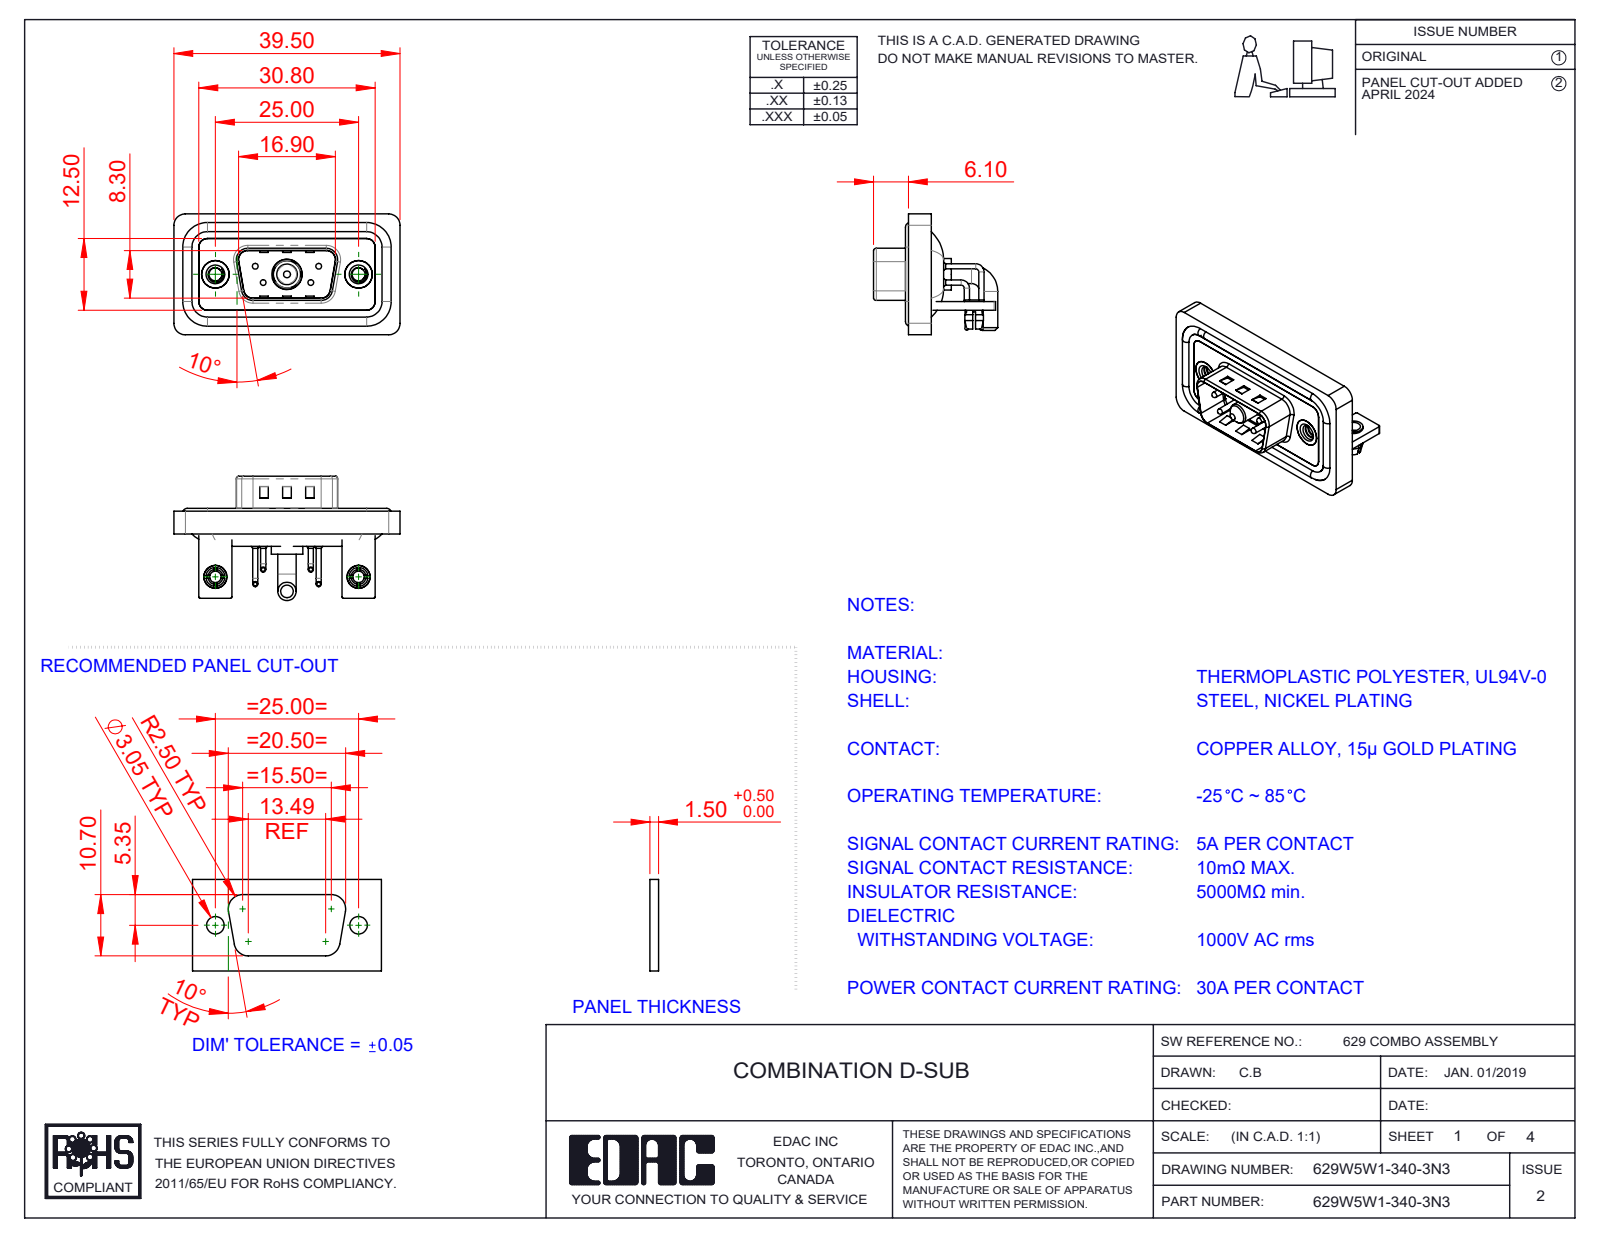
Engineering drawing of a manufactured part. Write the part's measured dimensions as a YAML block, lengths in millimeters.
part_name: "629Combo Waterproof Housing_09 Contacts; Power Pin_30A RA; 629Combo Housing_5W1; 629Combo Stabilizer Bracket (+7 more)"
step_written_by: "SolidWorks 2023 (CONFIG_CONTROL_DESIGN)"
units: millimeters
bodies: {solids: 17, faces: 1026, planar: 479, cylindrical: 395, other: 152}
overall_size: [39.5, 21.7, 21.1]
volume: 4818
surface_area: 7979
round_holes:
  - {diameter: 2, count: 6}
  - {diameter: 0.75, count: 4}
  - {diameter: 1.6, count: 4}
  - {diameter: 2.26, count: 2}
  - {diameter: 2.5, count: 2}
  - {diameter: 3.2, count: 2}
  - {diameter: 4, count: 2}
  - {diameter: 4.8, count: 2}
  - {diameter: 5, count: 2}
  - {diameter: 4.85, count: 1}
  - {diameter: 5.3, count: 1}
round_bosses_or_shafts:
  - {diameter: 0.9, count: 8}
  - {diameter: 1.6, count: 4}
  - {diameter: 1.5, count: 4}
  - {diameter: 1, count: 4}
  - {diameter: 0.65, count: 4}
  - {diameter: 4.9, count: 2}
  - {diameter: 4, count: 2}
  - {diameter: 3.4, count: 2}
partial_cylinders:
  - {radius: 2, count: 19}
  - {radius: 1.5, count: 18}
  - {radius: 0.25, count: 16}
  - {radius: 0.5, count: 9}
  - {radius: 1.6, count: 8}
  - {radius: 0.6, count: 4}
  - {radius: 0.65, count: 4}
  - {radius: 0.9, count: 4}
face_to_face_distances: [0.4, 1.5, 0.8, 2.9, 1.1, 2.1, 1.2, 1.6, 2.5, 3.7]
hole_center_spacings: [3.16, 5.72, 7.1, 12.5, 18.1, 25, 4.39, 4.4]
